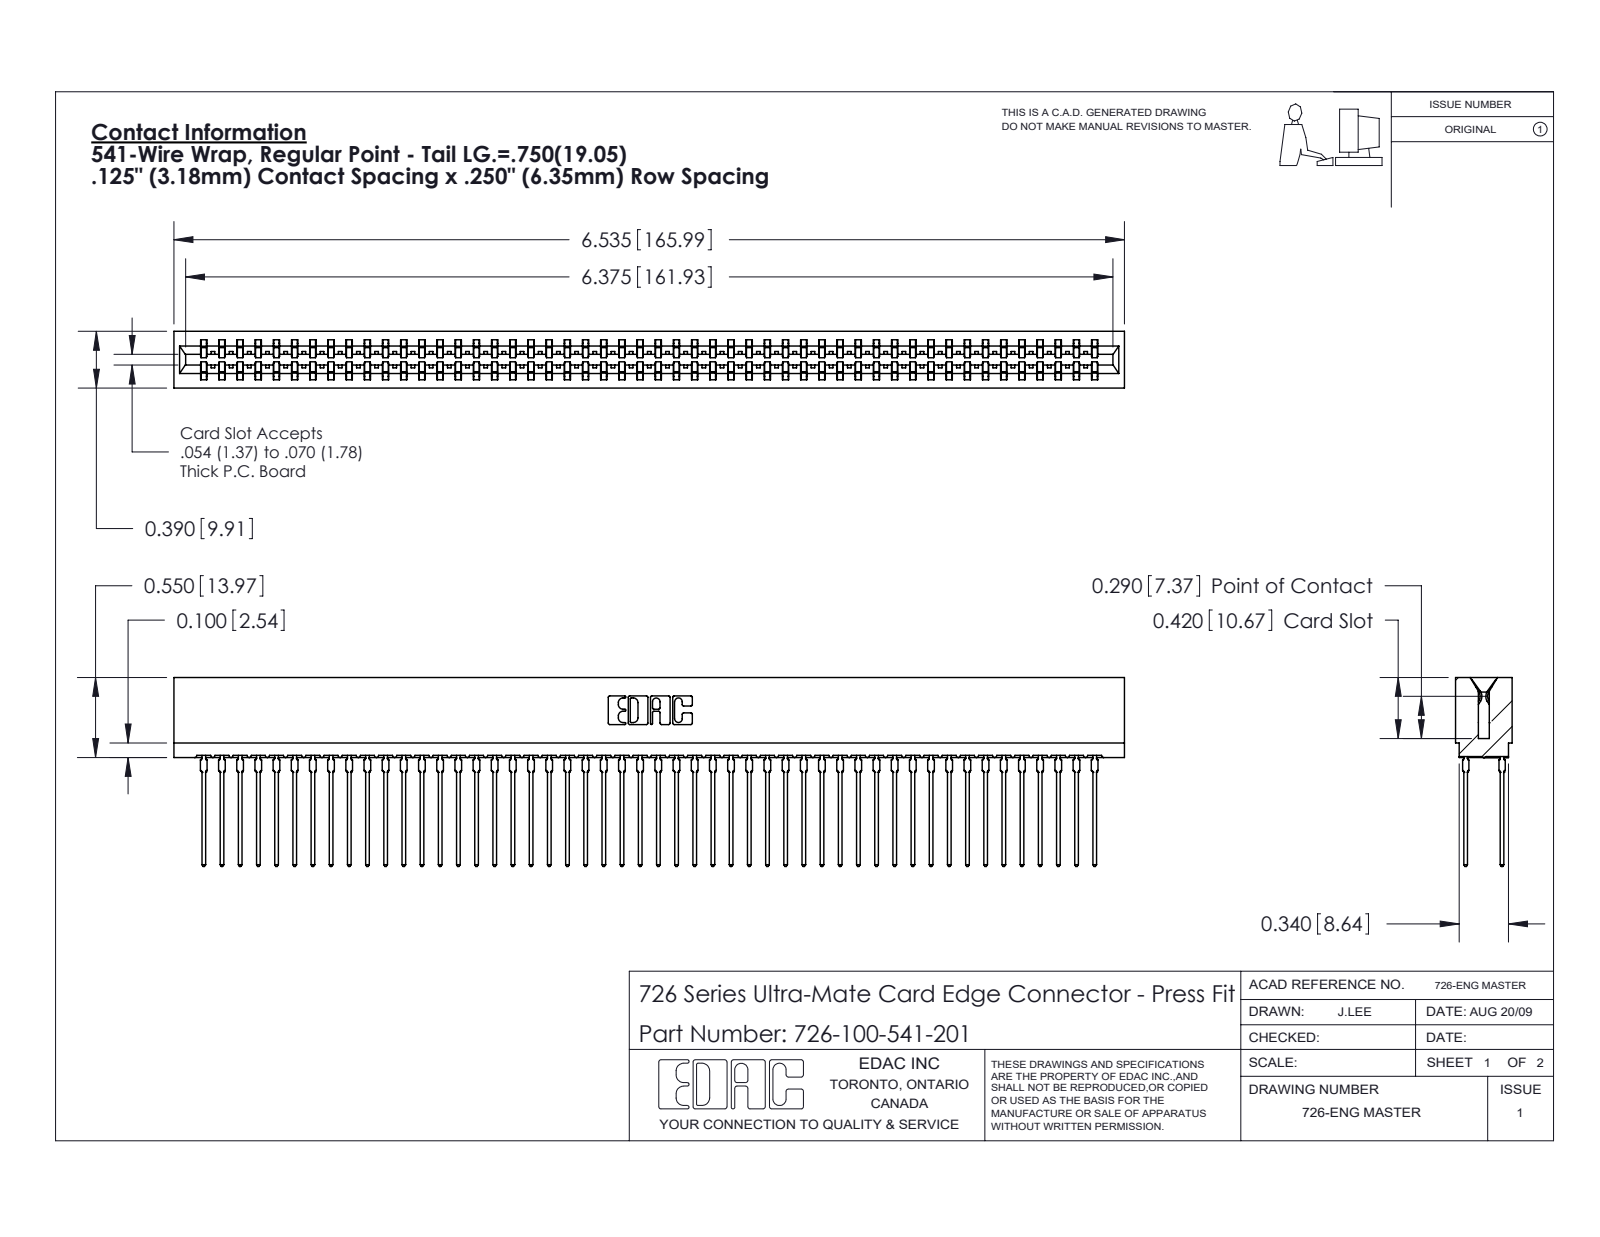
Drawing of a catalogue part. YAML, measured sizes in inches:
part_name: "726-100-541-201; 726 Part_.515 Slot Depth - 01; 746-292-001_541"
step_written_by: "SolidWorks 2020 (CONFIG_CONTROL_DESIGN)"
units: inches
bodies: {solids: 101, faces: 9047, planar: 4655, cylindrical: 1792, other: 2600}
overall_size: [6.535, 1.299, 0.39]
volume: 0.963
surface_area: 44.94
partial_cylinders:
  - {radius: 0.021, count: 200}
  - {radius: 0.015, count: 51}
  - {radius: 0.01, count: 22}
  - {radius: 0.005, count: 8}
  - {radius: 0.011, count: 8}
  - {radius: 0.007, count: 6}
  - {radius: 0.031, count: 6}
  - {radius: 0.026, count: 3}
face_to_face_distances: [0.057, 0.333, 0.025, 0.307, 0.25, 0.39, 0.083, 0.275, 0.225, 0.365]
